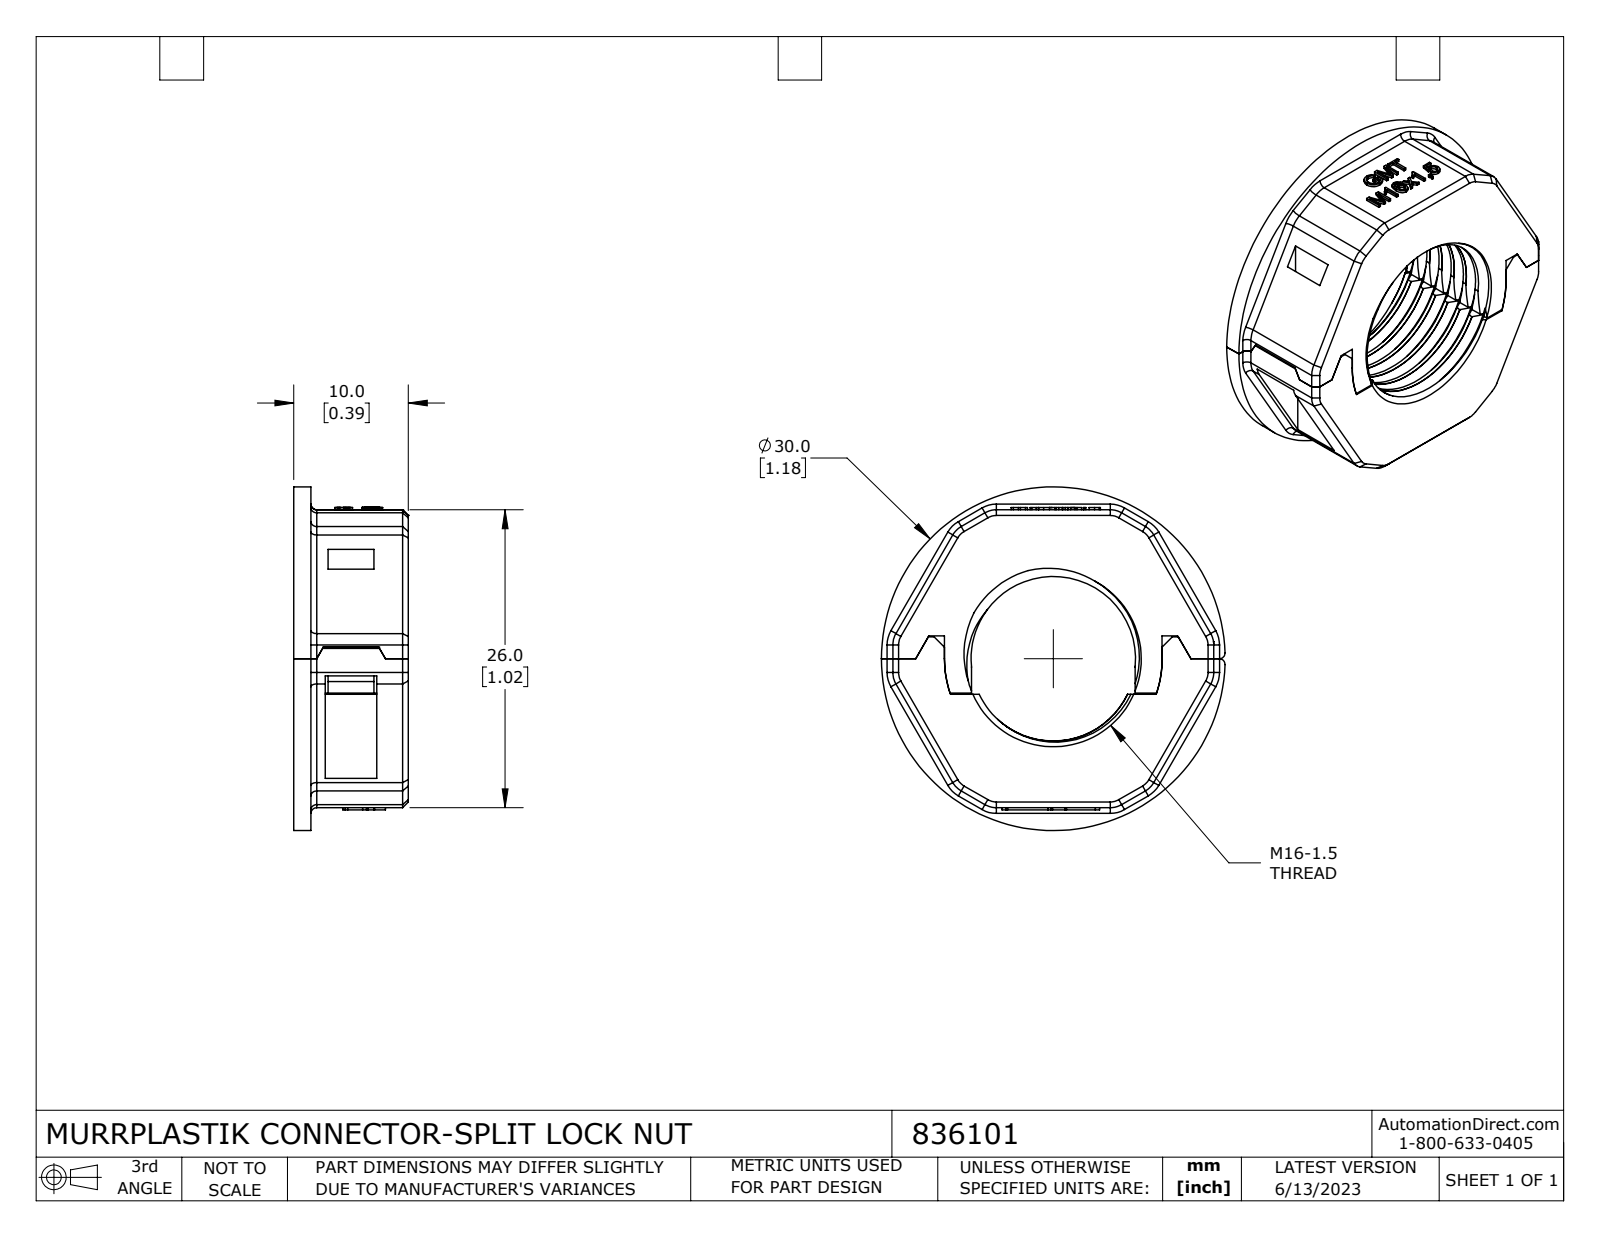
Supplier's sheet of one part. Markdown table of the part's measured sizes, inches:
| quantity | value |
| --- | --- |
| part name | 836101 |
| STEP written by | SolidWorks 2021 (CONFIG_CONTROL_DESIGN) |
| units | inches |
| bodies | 2 solids, 462 faces (233 planar, 85 cylindrical, 144 other) |
| overall size | 1.181 × 1.181 × 0.394 |
| volume | 0.235 in³ |
| surface area | 5.205 in² |
| round holes (diameter × count) | 0.236 × 1, 0.565 × 1, 0.63 × 1 |
| round bosses / shafts (diameter × count) | 1.181 × 1 |
| partial cylindrical surfaces (radius × count) | 0.02 × 14, 0.079 × 12, 0.004 × 2, 0.374 × 1 |
| main face-to-face distances | 0.394, 0.059, 1.024, 0.039, 0.285, 0.108, 0.335, 0.512, 0.748, 0.118 |
